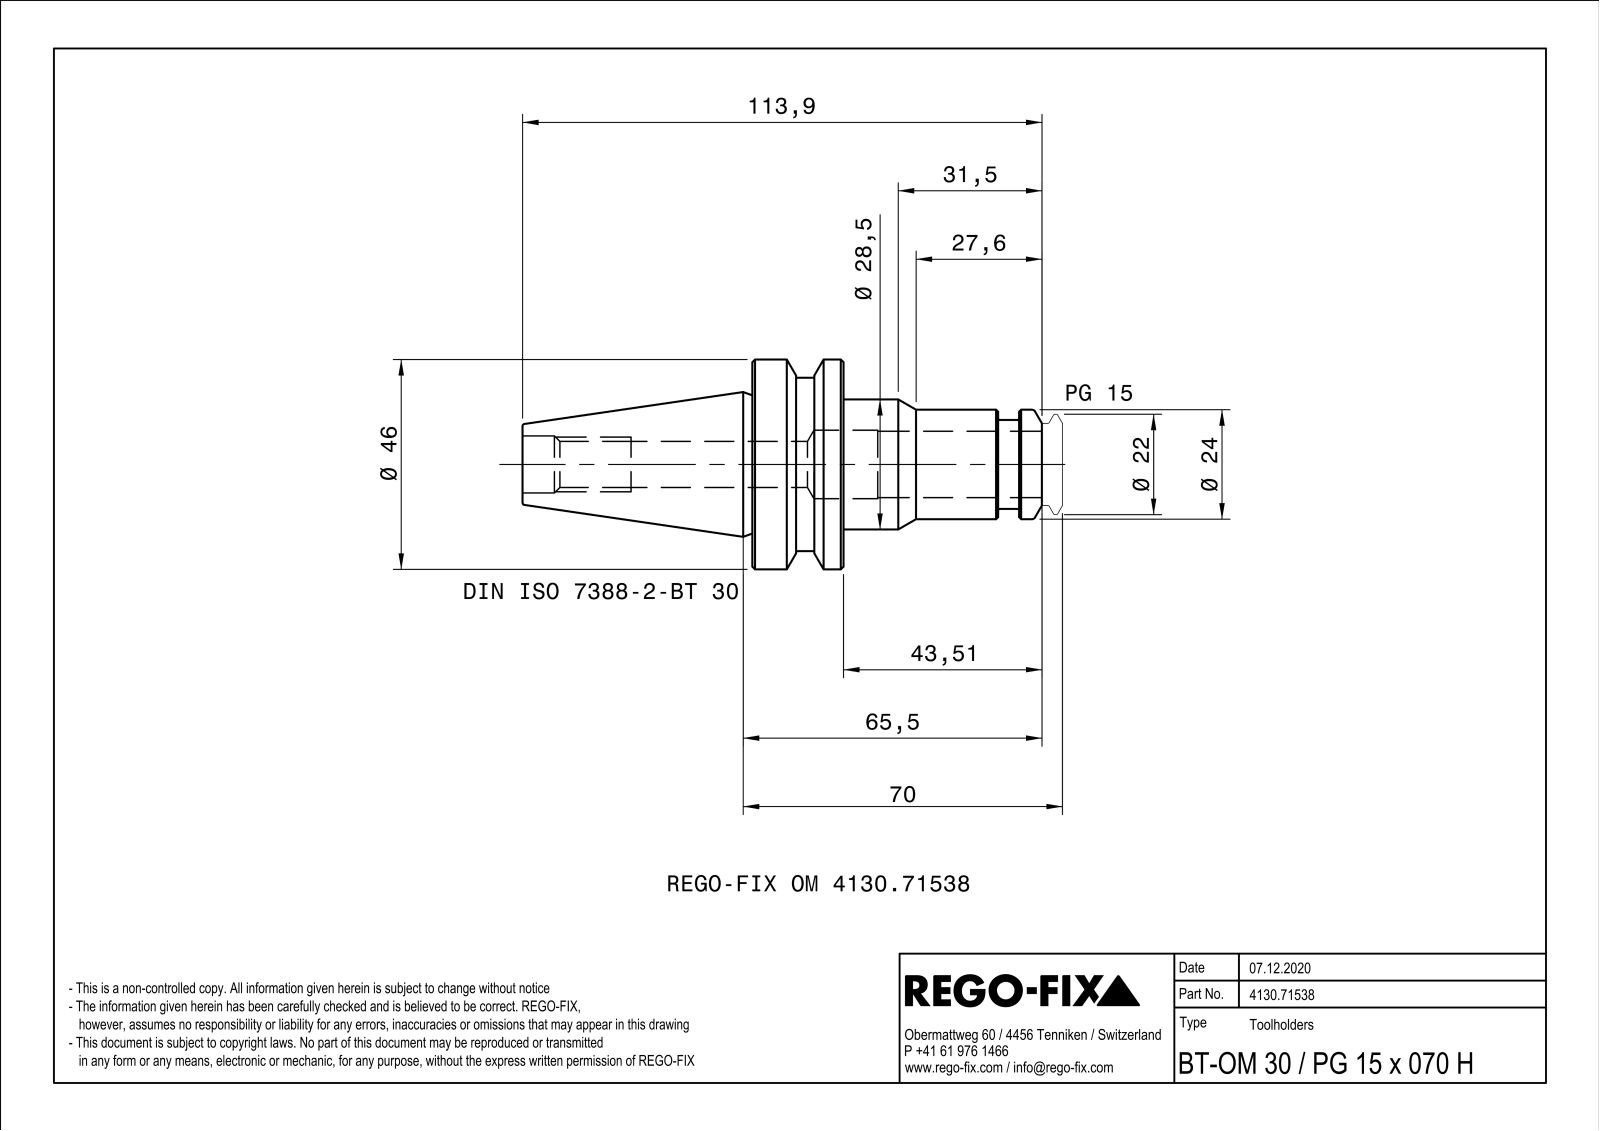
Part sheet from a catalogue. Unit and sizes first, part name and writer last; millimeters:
Units: millimetres
Overall size (bounding box): 113.9 × 46 × 46
Round holes (diameter × count): ⌀10.11 ×1, ⌀12.5 ×1, ⌀15 ×1
Round bosses / shafts (diameter × count): ⌀46 ×1, ⌀38 ×1, ⌀28.5 ×1, ⌀24 ×1, ⌀19.5 ×1
Main face-to-face distances: 20, 53.9, 33.9, 4.6, 38.5, 58.5, 108.9, 104.3, 70.4, 50.4
Volume: 62 539 mm³ · Surface area: 17 685 mm²
Bodies: 1 solid, 53 faces (9 planar, 13 cylindrical, 31 other)
Part name (STEP PRODUCT): NOCUT
STEP written by: SIEMENS PLM Software Solid Edge ST10 (AUTOMOTIVE_DESIGN)
